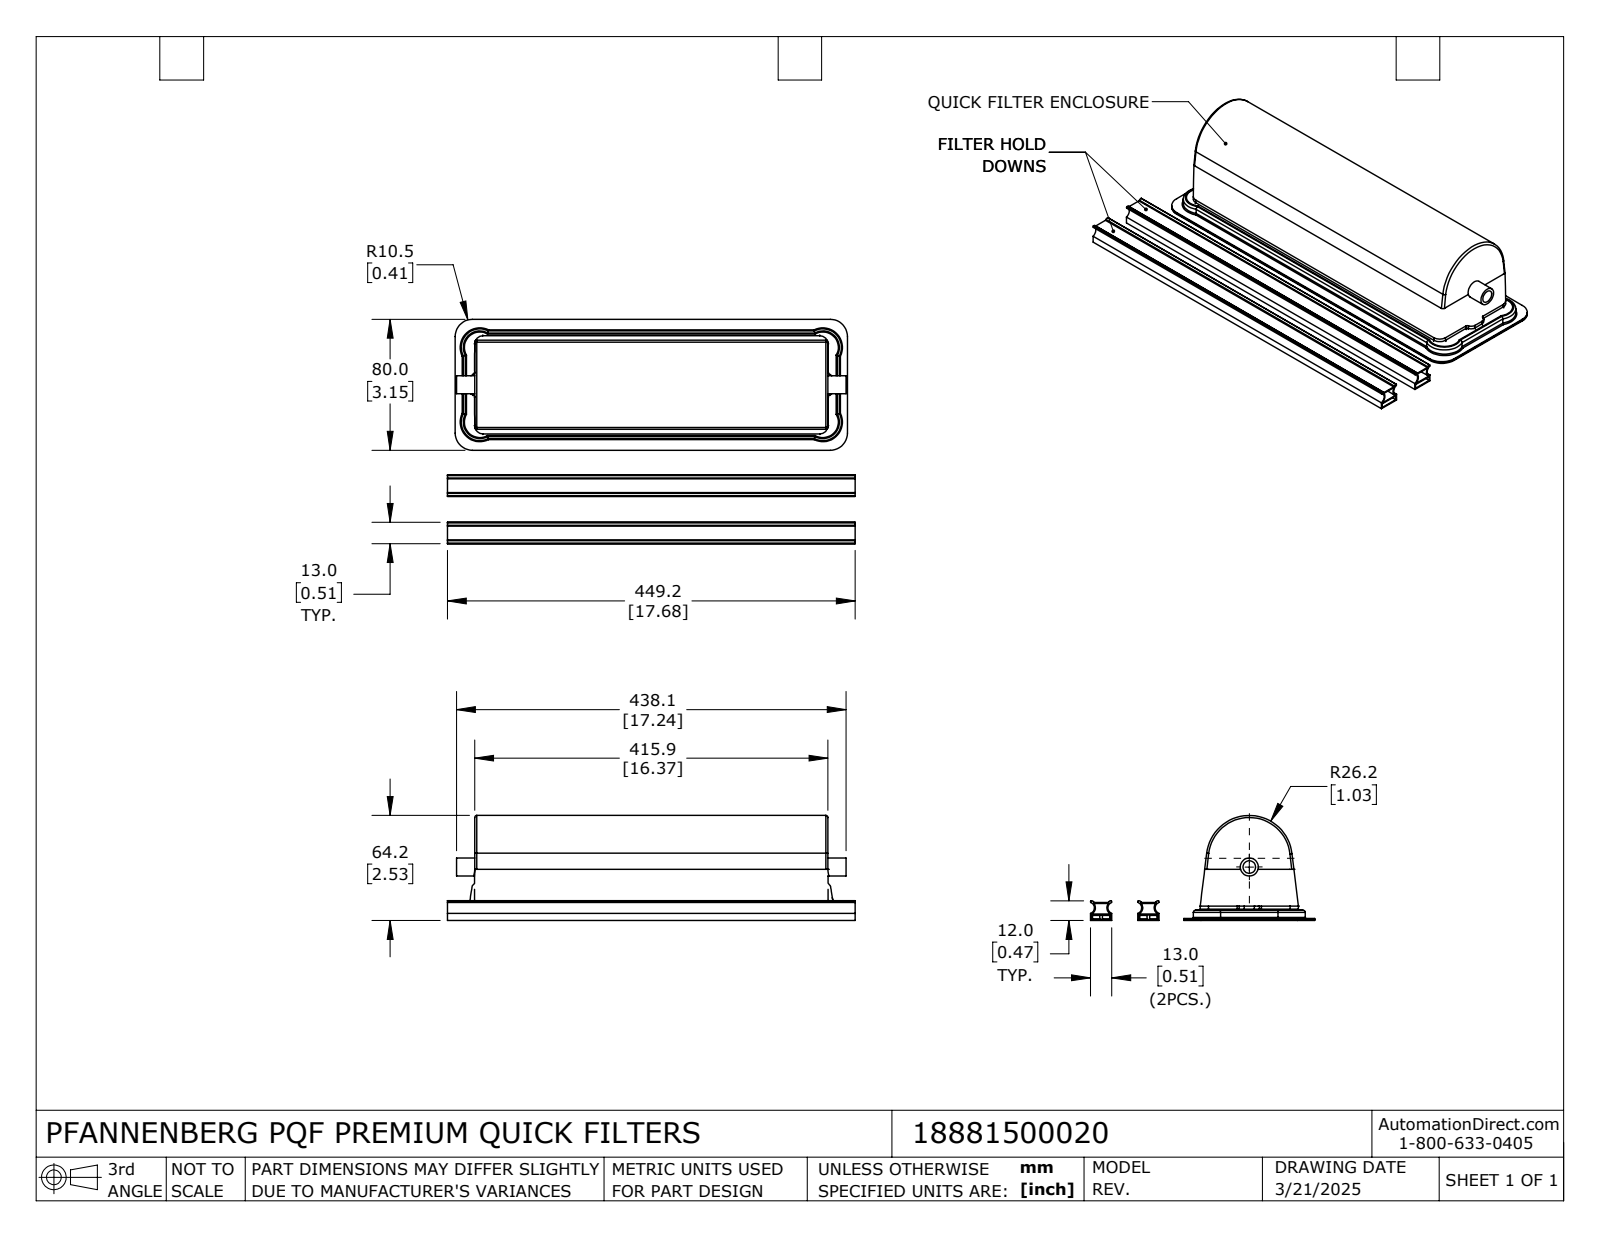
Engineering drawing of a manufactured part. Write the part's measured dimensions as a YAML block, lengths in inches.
part_name: "18881500020"
step_written_by: "SolidWorks 2024 (AUTOMOTIVE_DESIGN)"
units: inches
bodies: {solids: 13, faces: 600, planar: 140, cylindrical: 268, other: 192}
overall_size: [17.686, 5.395, 2.527]
volume: 57.05
surface_area: 739.5
round_holes:
  - {diameter: 0.413, count: 4}
  - {diameter: 0.303, count: 1}
  - {diameter: 0.433, count: 1}
round_bosses_or_shafts:
  - {diameter: 0.063, count: 8}
  - {diameter: 0.463, count: 4}
  - {diameter: 0.413, count: 4}
  - {diameter: 2, count: 1}
partial_cylinders:
  - {radius: 0.025, count: 42}
  - {radius: 0.05, count: 42}
  - {radius: 0.197, count: 12}
  - {radius: 0.222, count: 8}
  - {radius: 0.397, count: 8}
  - {radius: 0.422, count: 8}
  - {radius: 0.446, count: 8}
  - {radius: 0.02, count: 4}
face_to_face_distances: [0.025, 0.132, 0.107, 0.41, 0.278, 0.209, 0.078, 0.201, 0.385, 0.223]
hole_center_spacings: [5.323, 7.874, 2.551, 13.197]
